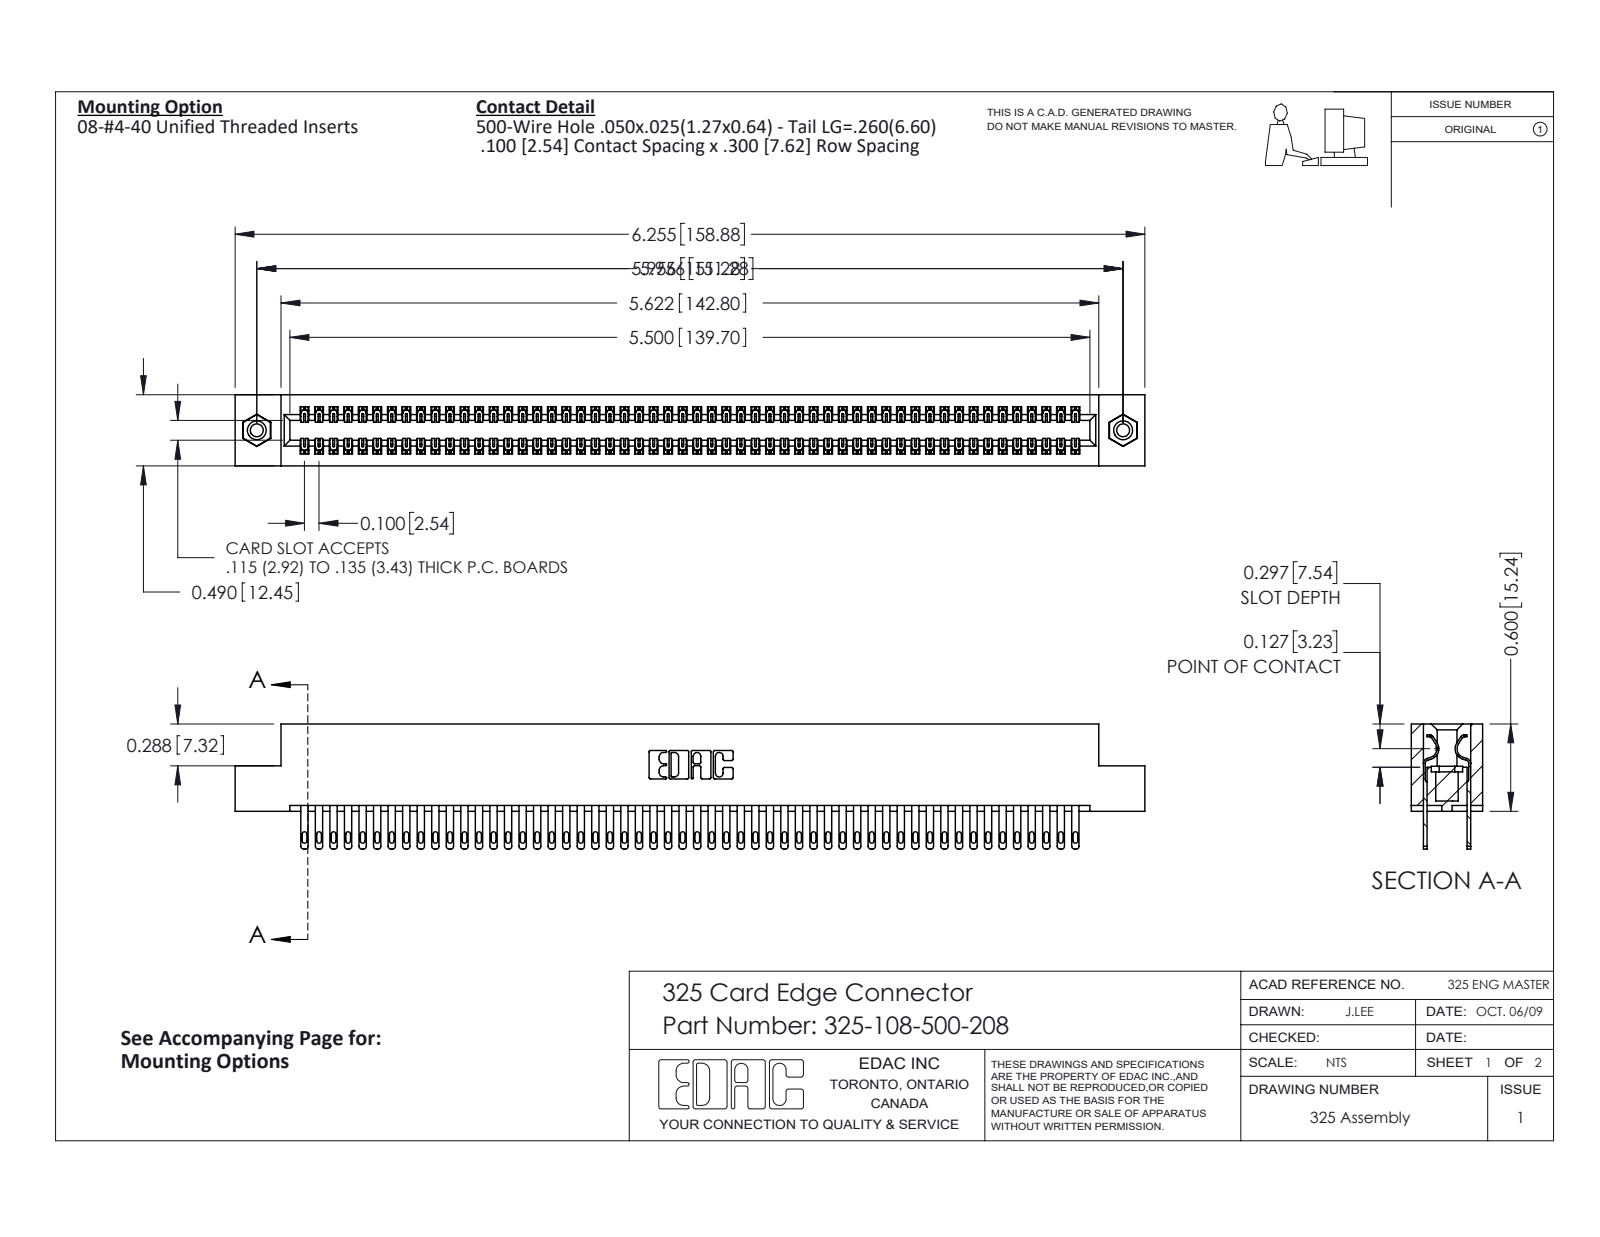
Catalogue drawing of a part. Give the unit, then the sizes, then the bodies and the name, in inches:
Units: inches
Overall size (bounding box): 6.255 × 0.86 × 0.49
Round holes (diameter × count): ⌀0.089 ×2, ⌀0.125 ×2, ⌀0.16 ×2
Round bosses / shafts (diameter × count): ⌀0.155 ×2
Partial cylindrical surfaces — rounded edges, fillets, slot ends (radius × count): R0.006 ×162, R0.016 ×108, R0.02 ×108, R0.01 ×22, R0.007 ×6, R0.031 ×6, R0.026 ×3, R0.014 ×2
Main face-to-face distances: 0.083, 0.407, 0.3, 0.107, 0.383, 0.025, 0.49, 0.325, 0.275, 0.56
Hole centre spacings: 5.956
Volume: 1.278 in³ · Surface area: 41.5 in²
Bodies: 111 solids, 5358 faces (3342 planar, 2000 cylindrical, 16 other)
Part name (STEP PRODUCT): 325-292-001_325-293-100; 345-250-001_345-250-003-102; 325 Part_TI; 325-108-500-208
STEP written by: SolidWorks 2016 (CONFIG_CONTROL_DESIGN)
